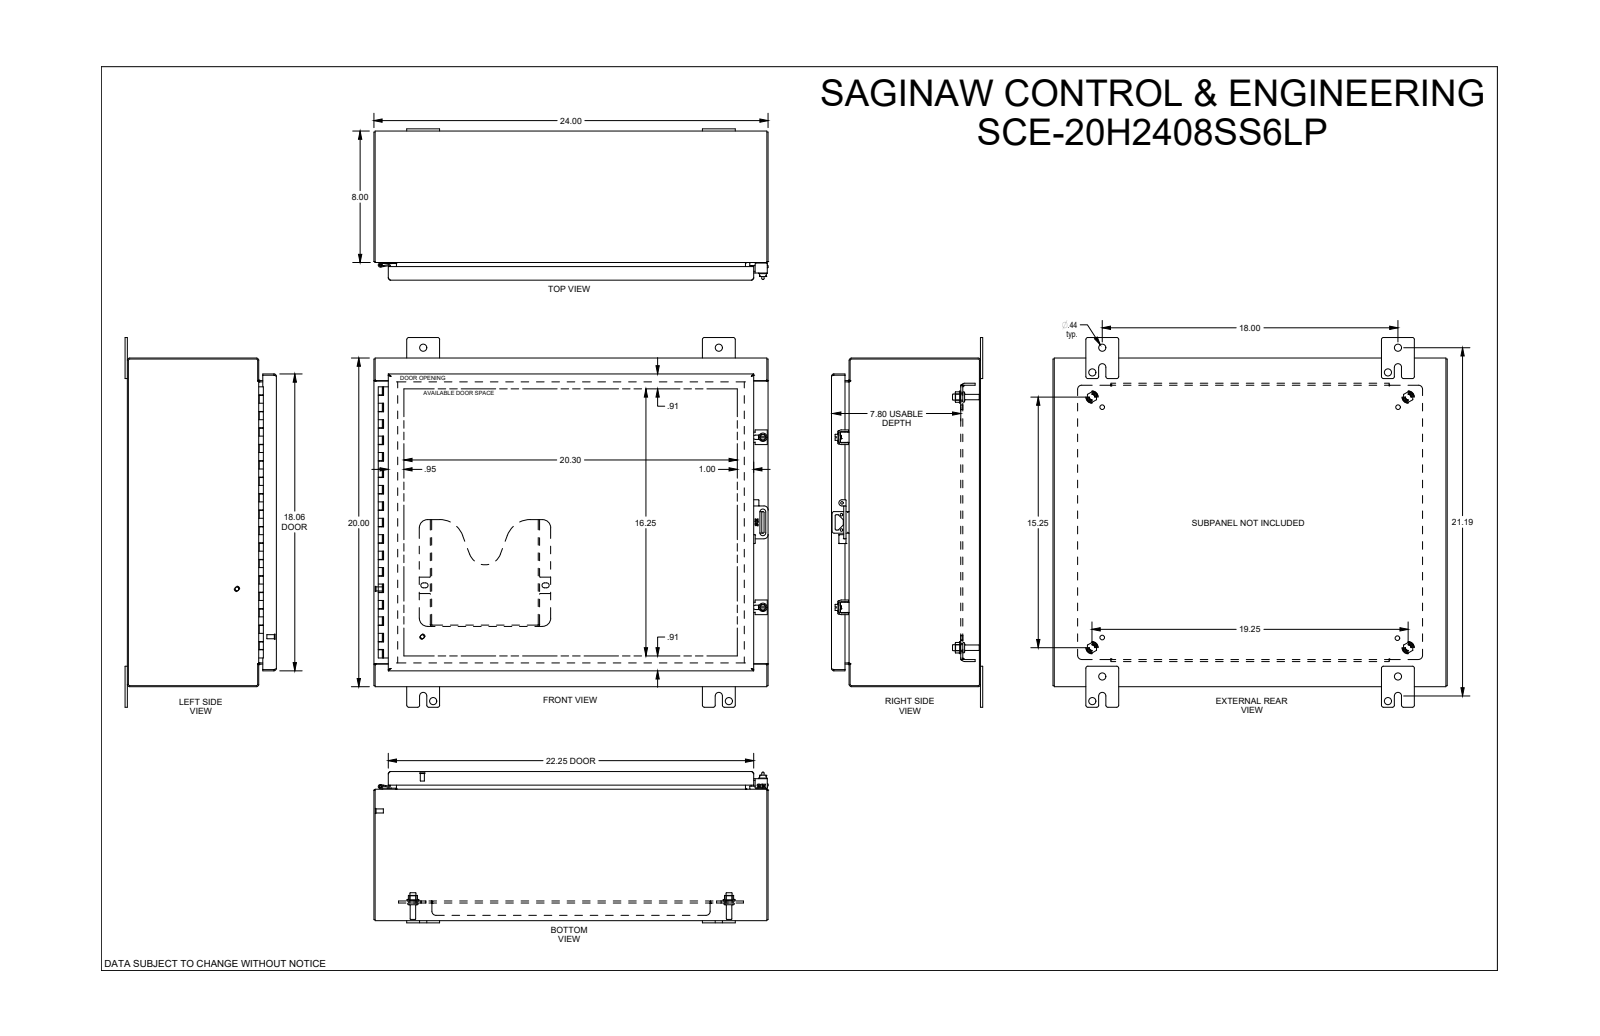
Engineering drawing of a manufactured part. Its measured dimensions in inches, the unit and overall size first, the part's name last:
Units: inches
Overall size (bounding box): 24 × 22.5 × 9.208
Round holes (diameter × count): ⌀0.437 ×8, ⌀0.25 ×5, ⌀0.281 ×4, ⌀0.367 ×4, ⌀0.5 ×4, ⌀0.19 ×3, ⌀0.193 ×3, ⌀0.16 ×2, ⌀0.203 ×2, ⌀0.13 ×1, ⌀0.132 ×1
Round bosses / shafts (diameter × count): ⌀0.248 ×7, ⌀0.563 ×5, ⌀0.366 ×4, ⌀0.332 ×4, ⌀0.256 ×3, ⌀0.25 ×3, ⌀0.188 ×3, ⌀0.507 ×2
Partial cylindrical surfaces — rounded edges, fillets, slot ends (radius × count): R0.01 ×108, R0.015 ×36, R0.029 ×30, R0.03 ×27, R0.125 ×27, R0.06 ×25, R0.04 ×22, R0.07 ×14
Main face-to-face distances: 0.075, 8.998, 8.923, 0.075, 8.998, 9.073, 19.925, 7.923, 1.2, 1.125
Hole centre spacings: 0.875, 18, 26.907, 14.644, 18.641, 23.689, 0.516, 1.439
Bodies: 0 solids, 3049 faces (1222 planar, 632 cylindrical, 1195 other)
Part name (STEP PRODUCT): SCE-20H2408SS6LP
STEP written by: SolidWorks 2019 (CONFIG_CONTROL_DESIGN)
